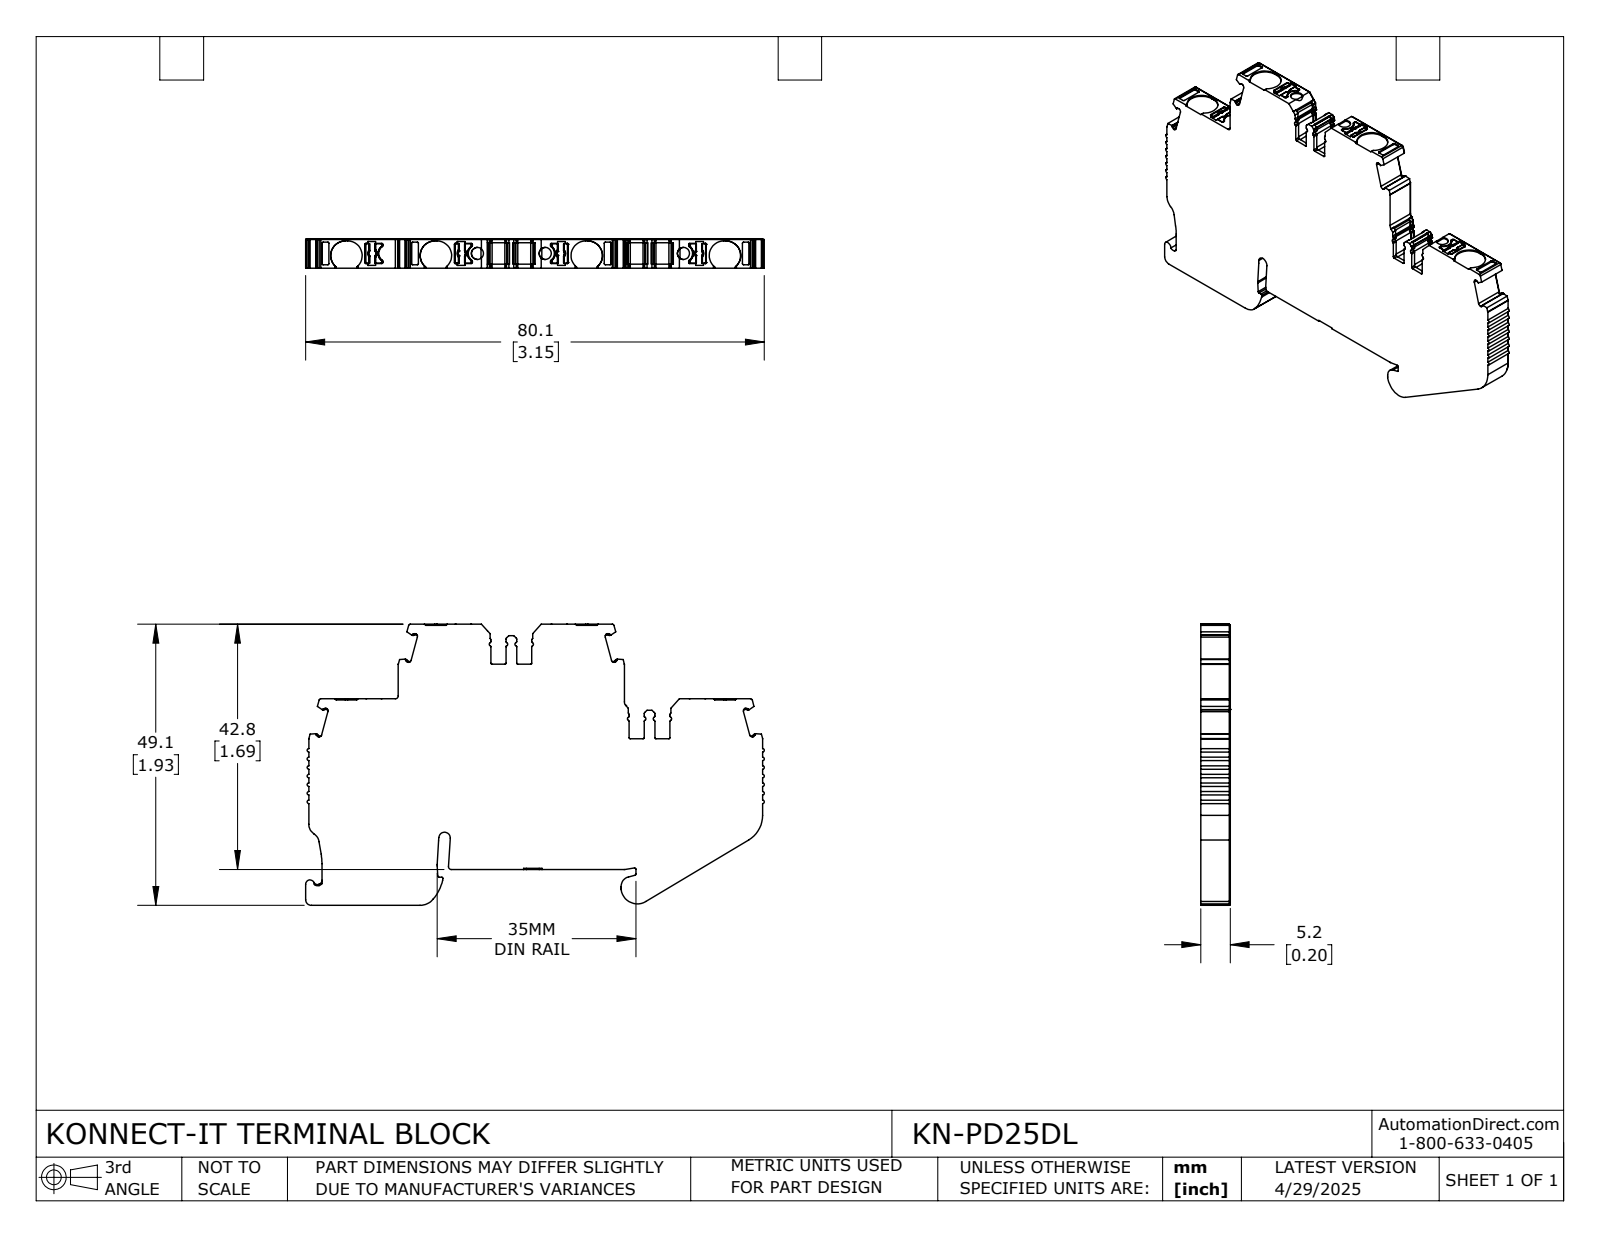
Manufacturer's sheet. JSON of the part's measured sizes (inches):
{"part_name": "KN-PD25DL", "step_written_by": "SolidWorks 2024 (CONFIG_CONTROL_DESIGN)", "units": "inches", "bodies": {"solids": 1, "faces": 979, "planar": 470, "cylindrical": 438, "other": 71}, "overall_size": [3.153, 1.933, 0.203], "volume_in3": 0.889, "surface_area_in2": 11.63, "round_holes": [[0.083, 3]], "partial_cylinders_radius": [[0.008, 100], [0.012, 57], [0.004, 41], [0.02, 21], [0.016, 17], [0.006, 16], [0.024, 9], [0.006, 8]], "face_to_face_distances": [0.203, 0.512, 0.246, 1.678, 1.166, 1.924, 0.079, 1.412, 0.504, 0.95], "hole_center_spacings": [0.466, 0.95, 1.417]}
